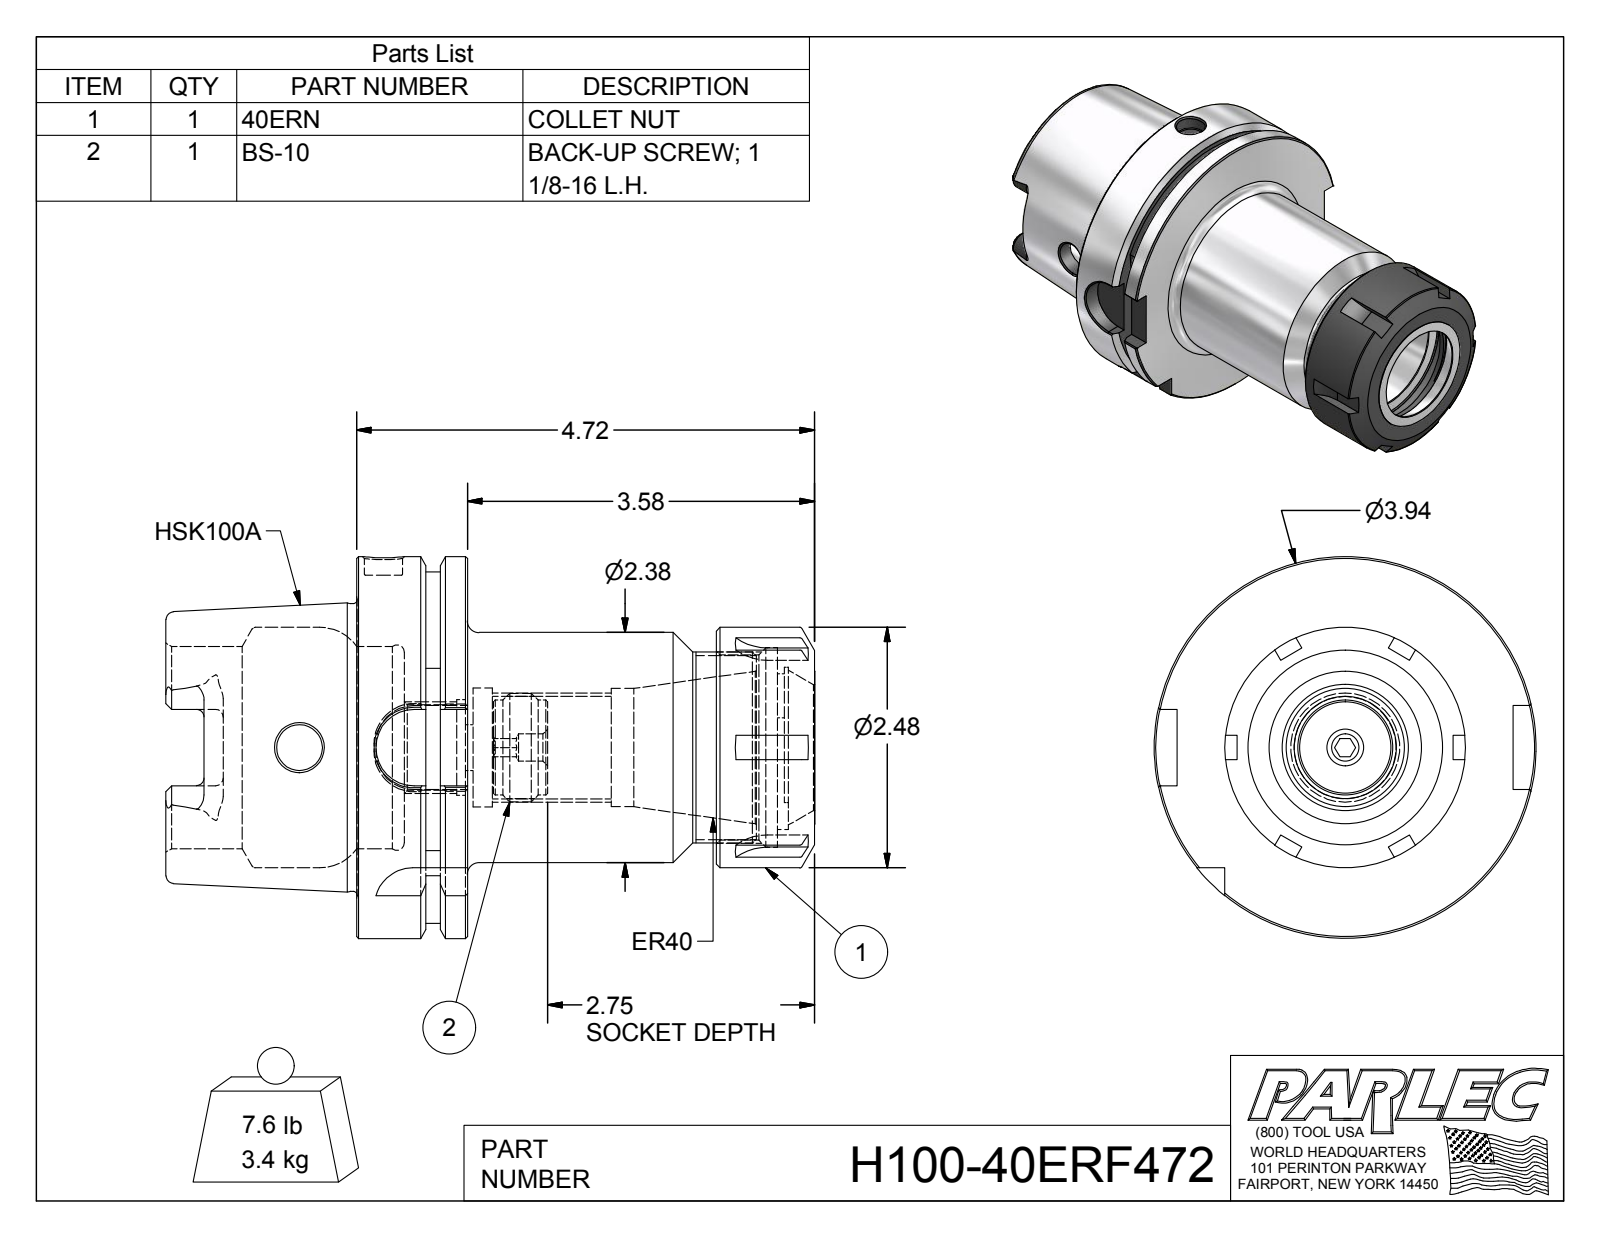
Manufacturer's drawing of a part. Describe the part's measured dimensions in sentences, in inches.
The part is named "H100-40ERF472; H100-40ER5-1; 40ERN; BS-10". Its 3-D file was written by "Autodesk Inventor 2012 (AUTOMOTIVE_DESIGN)". It is 3 solids with 199 faces: 77 planar, 55 cylindrical and 67 other. Overall it measures 6.694 by 3.937 by 3.937 inches. Its volume is 26.66 cubic inches and its surface area 133 square inches. Round holes: 2 of diameter 0.472, 1 of diameter 0.22, 1 of diameter 0.28, 1 of diameter 0.394, 1 of diameter 0.881, 1 of diameter 0.985, 1 of diameter 1.057, 1 of diameter 1.22, 1 of diameter 1.225, 1 of diameter 1.298, 1 of diameter 1.909, 1 of diameter 2.057. Round bosses or shafts: 1 of diameter 3.937, 1 of diameter 2.967, 1 of diameter 2.375, 1 of diameter 1.969, 1 of diameter 1.575, 1 of diameter 1.118, 1 of diameter 0.98. Partial cylindrical surfaces (rounded edges, fillets, slot ends): 6 of radius 0.079, 6 of radius 0.501, 4 of radius 0.192, 4 of radius 0.394, 1 of radius 0.762, 1 of radius 0.787, 1 of radius 0.827, 1 of radius 1.811. The main face-to-face distances are 1.142, 0.492, 0.65, 3.216, 0.63, 3.708, 2.567, 1.969, 2.461, 3.11.
